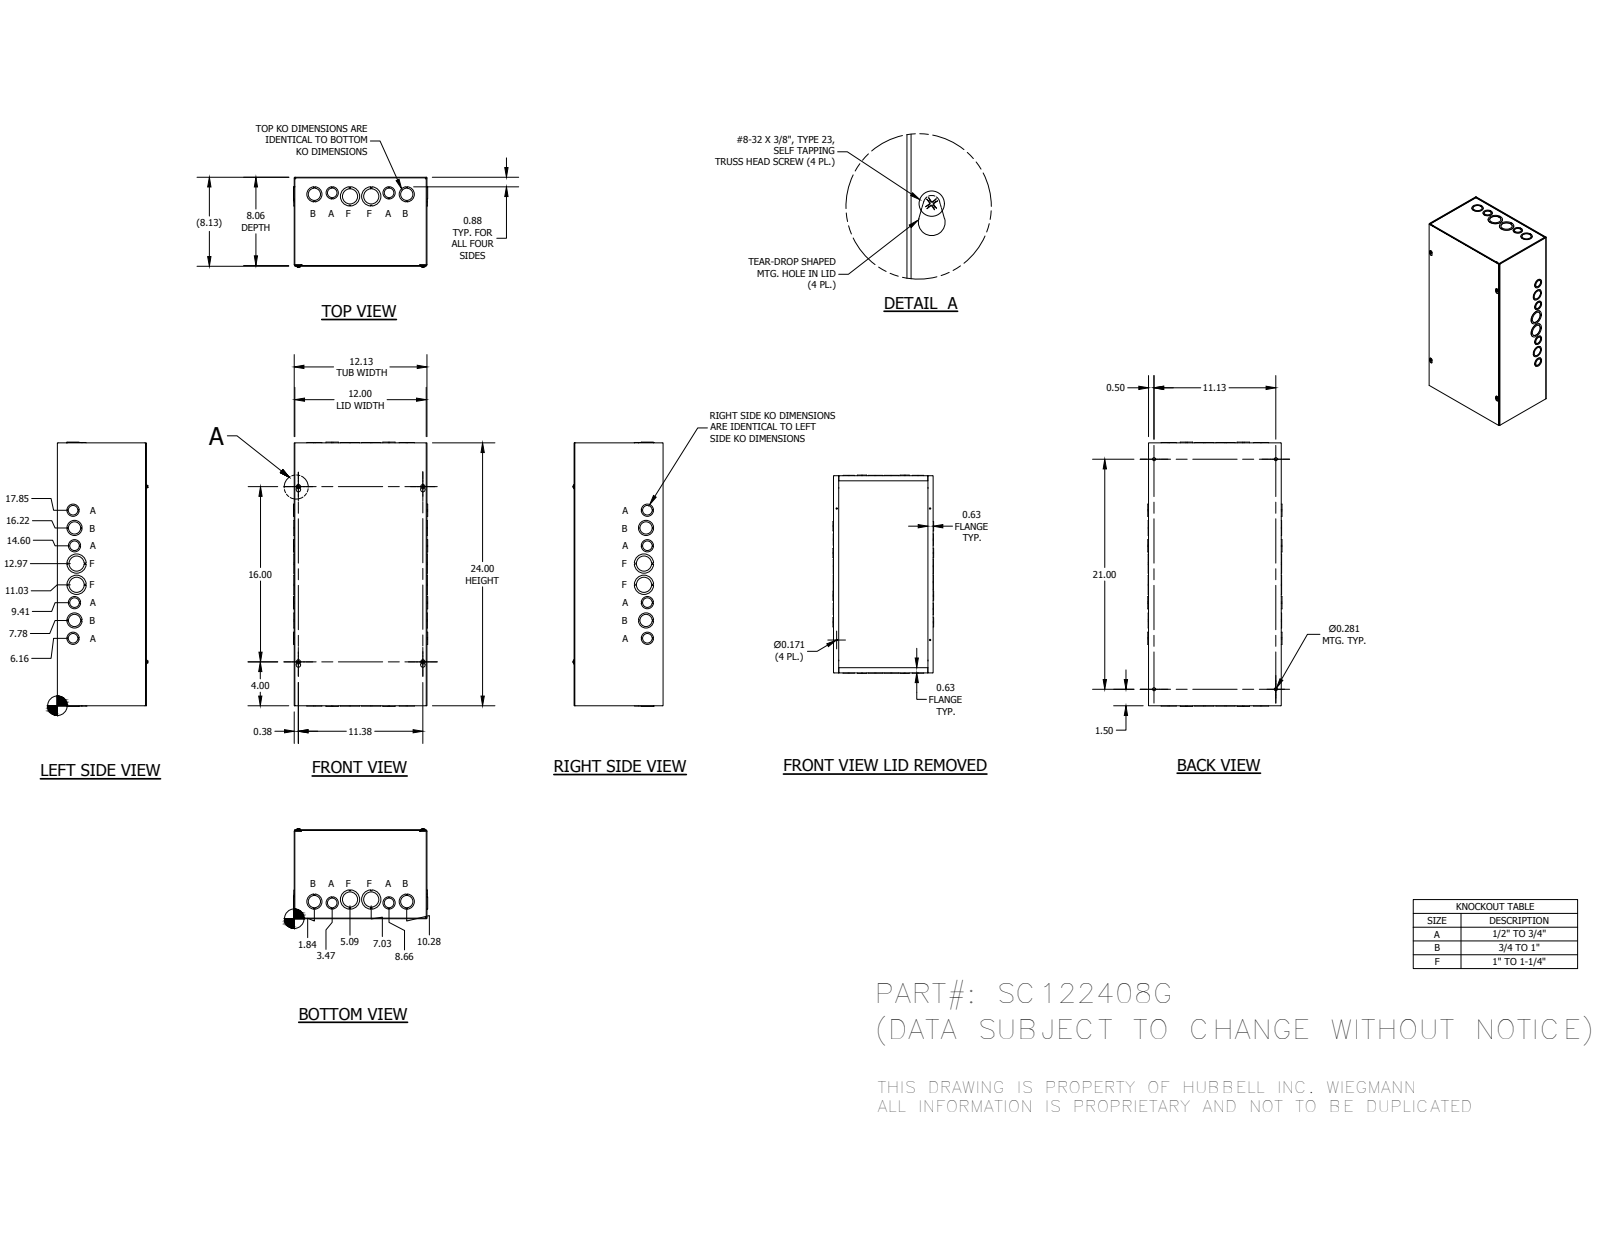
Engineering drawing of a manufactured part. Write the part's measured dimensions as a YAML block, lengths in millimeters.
part_name: "SC122408GBLR; SC1208GTB; SC1224GLPA; 34056 (+1 more)"
step_written_by: "Autodesk Inventor 2014 (AUTOMOTIVE_DESIGN)"
units: millimeters
bodies: {solids: 29, faces: 1055, planar: 771, cylindrical: 216, other: 68}
overall_size: [612.77, 311.15, 208.92]
round_holes:
  - {diameter: 28.57, count: 12}
  - {diameter: 22.22, count: 8}
  - {diameter: 34.92, count: 8}
  - {diameter: 4.34, count: 4}
  - {diameter: 7.14, count: 4}
  - {diameter: 44.45, count: 4}
round_bosses_or_shafts:
  - {diameter: 9.75, count: 4}
  - {diameter: 4.17, count: 4}
partial_cylinders:
  - {radius: 0.4, count: 12}
  - {radius: 1.98, count: 12}
  - {radius: 3.17, count: 4}
  - {radius: 5.16, count: 4}
face_to_face_distances: [1.59, 306.39, 203.2, 1.58, 204.79, 204.78, 206.37, 304.8, 307.98, 608.01]
hole_center_spacings: [41.4, 42.03, 63.58, 82.69, 90.9, 131.92, 173.13, 292.72]
